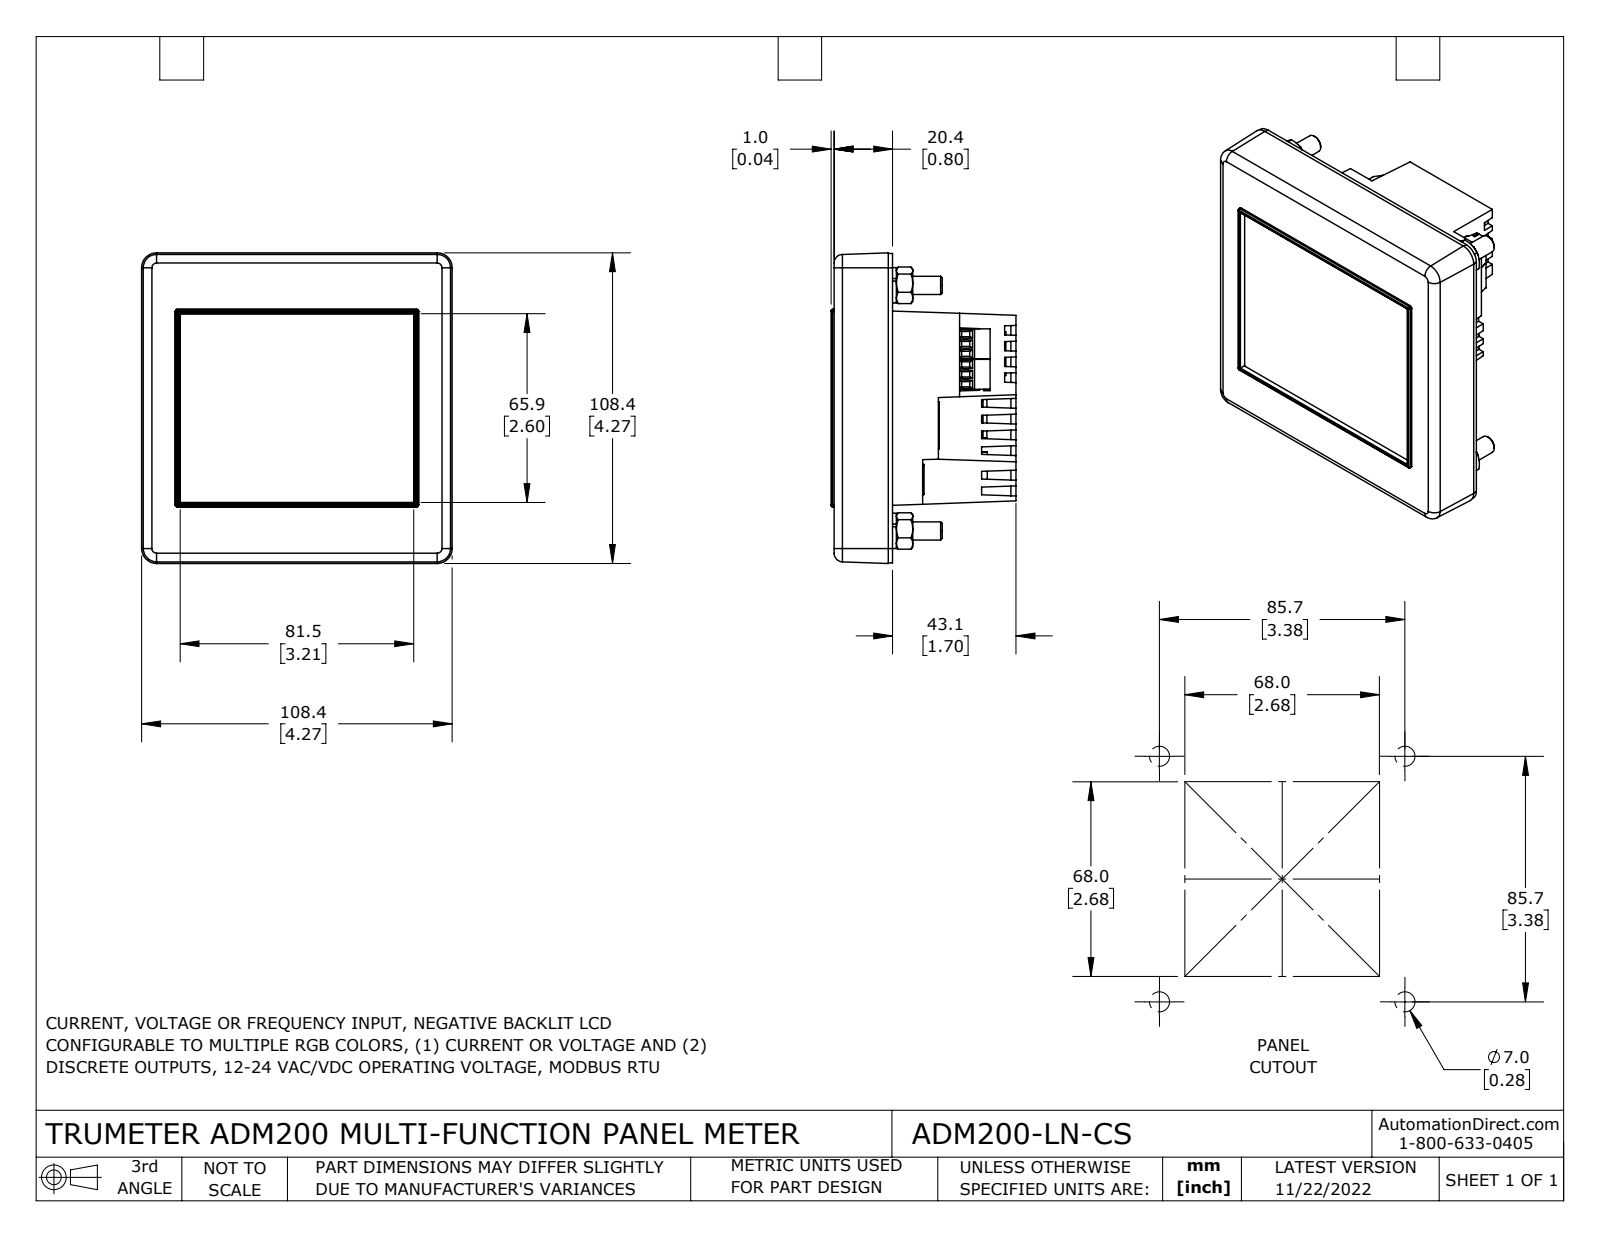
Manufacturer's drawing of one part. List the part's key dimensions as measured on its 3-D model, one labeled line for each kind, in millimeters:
Part name (STEP PRODUCT): ADM200-LN-CS
STEP written by: SolidWorks 2021 (CONFIG_CONTROL_DESIGN)
Units: millimetres
Bodies: 23 solids, 2059 faces (1384 planar, 290 cylindrical, 385 other)
Overall size (bounding box): 108.4 × 108.4 × 64.5
Volume: 128 000 mm³ · Surface area: 123 100 mm²
Round holes (diameter × count): ⌀1.8 ×9, ⌀2.9 ×6, ⌀3 ×5, ⌀5.4 ×4, ⌀6.4 ×4, ⌀6.6 ×4, ⌀7.5 ×4, ⌀3.9 ×2
Round bosses / shafts (diameter × count): ⌀1 ×5, ⌀12.4 ×4, ⌀11.1 ×4, ⌀0.6 ×4, ⌀2 ×2
Partial cylindrical surfaces — rounded edges, fillets, slot ends (radius × count): R0.2 ×32, R0.5 ×30, R1 ×7, R0.4 ×4, R0.8 ×4, R3 ×4, R5 ×4, R0.1 ×2
Main face-to-face distances: 0.8, 16.1, 2.8, 1.9, 1.5, 2, 17.6, 86.2, 88.1, 1.2
Hole centre spacings: 18, 82, 3.5, 7.4, 25, 36, 54, 60.9
